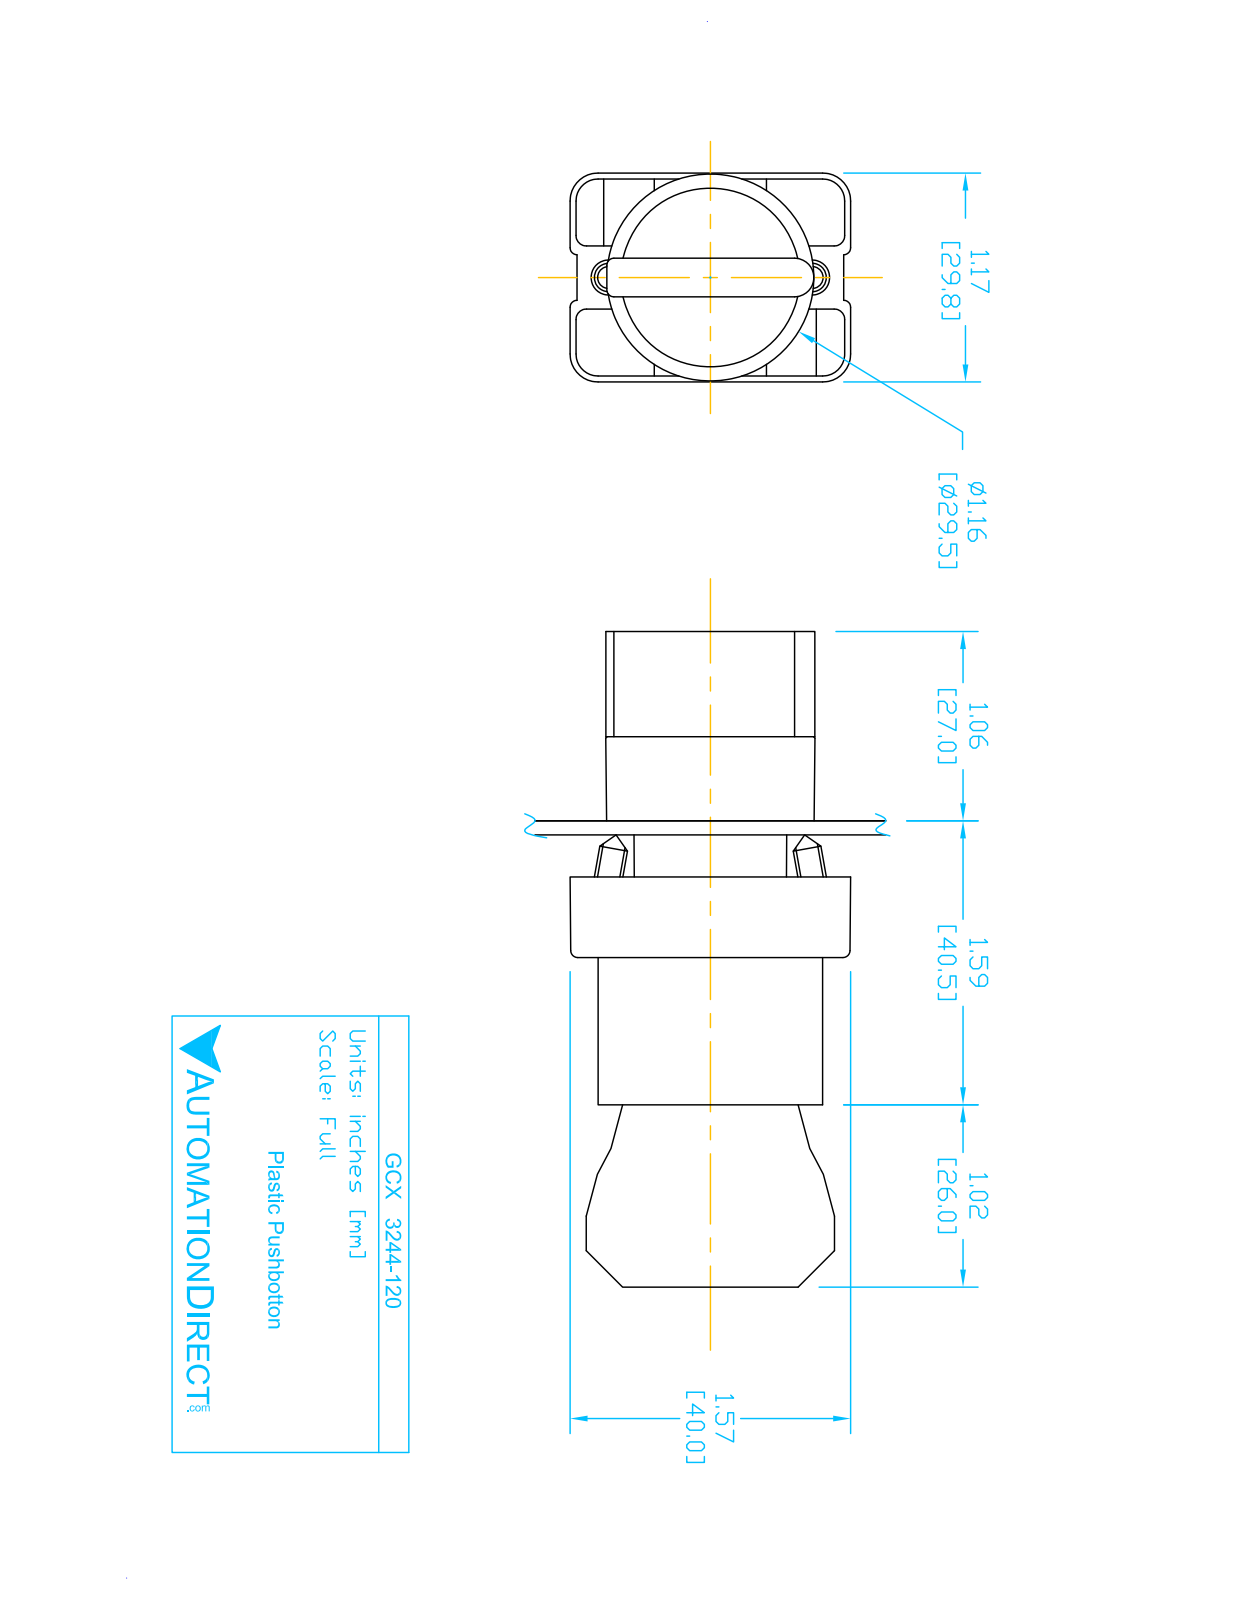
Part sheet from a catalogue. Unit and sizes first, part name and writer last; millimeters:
Units: millimetres
Overall size (bounding box): 92.8 × 40.2 × 29.9
Round holes (diameter × count): ⌀2 ×2, ⌀3.1 ×2, ⌀3.3 ×2, ⌀2.2 ×1, ⌀5 ×1, ⌀11.9 ×1, ⌀22.3 ×1, ⌀22.6 ×1, ⌀26 ×1
Round bosses / shafts (diameter × count): ⌀4 ×4, ⌀29.8 ×1, ⌀25.5 ×1, ⌀24 ×1, ⌀21.7 ×1, ⌀19.8 ×1, ⌀12.8 ×1
Partial cylindrical surfaces — rounded edges, fillets, slot ends (radius × count): R1.5 ×24, R1 ×12, R3.1 ×12, R4 ×12, R1 ×9, R3.3 ×2, R0.5 ×1, R1.6 ×1
Main face-to-face distances: 21, 51.3, 30.3, 14.7, 31.6, 29.7, 12, 11.9, 0.8, 0.8
Hole centre spacings: 6, 13.8, 12, 12.4
Volume: 45 870 mm³ · Surface area: 25 160 mm²
Bodies: 8 solids, 445 faces (263 planar, 151 cylindrical, 31 other)
Part name (STEP PRODUCT): ECX3029-2; GCX3244-120; GCX3244 OPERATOR; ecx1040 (+1 more)
STEP written by: SolidWorks 2016 (AUTOMOTIVE_DESIGN)
